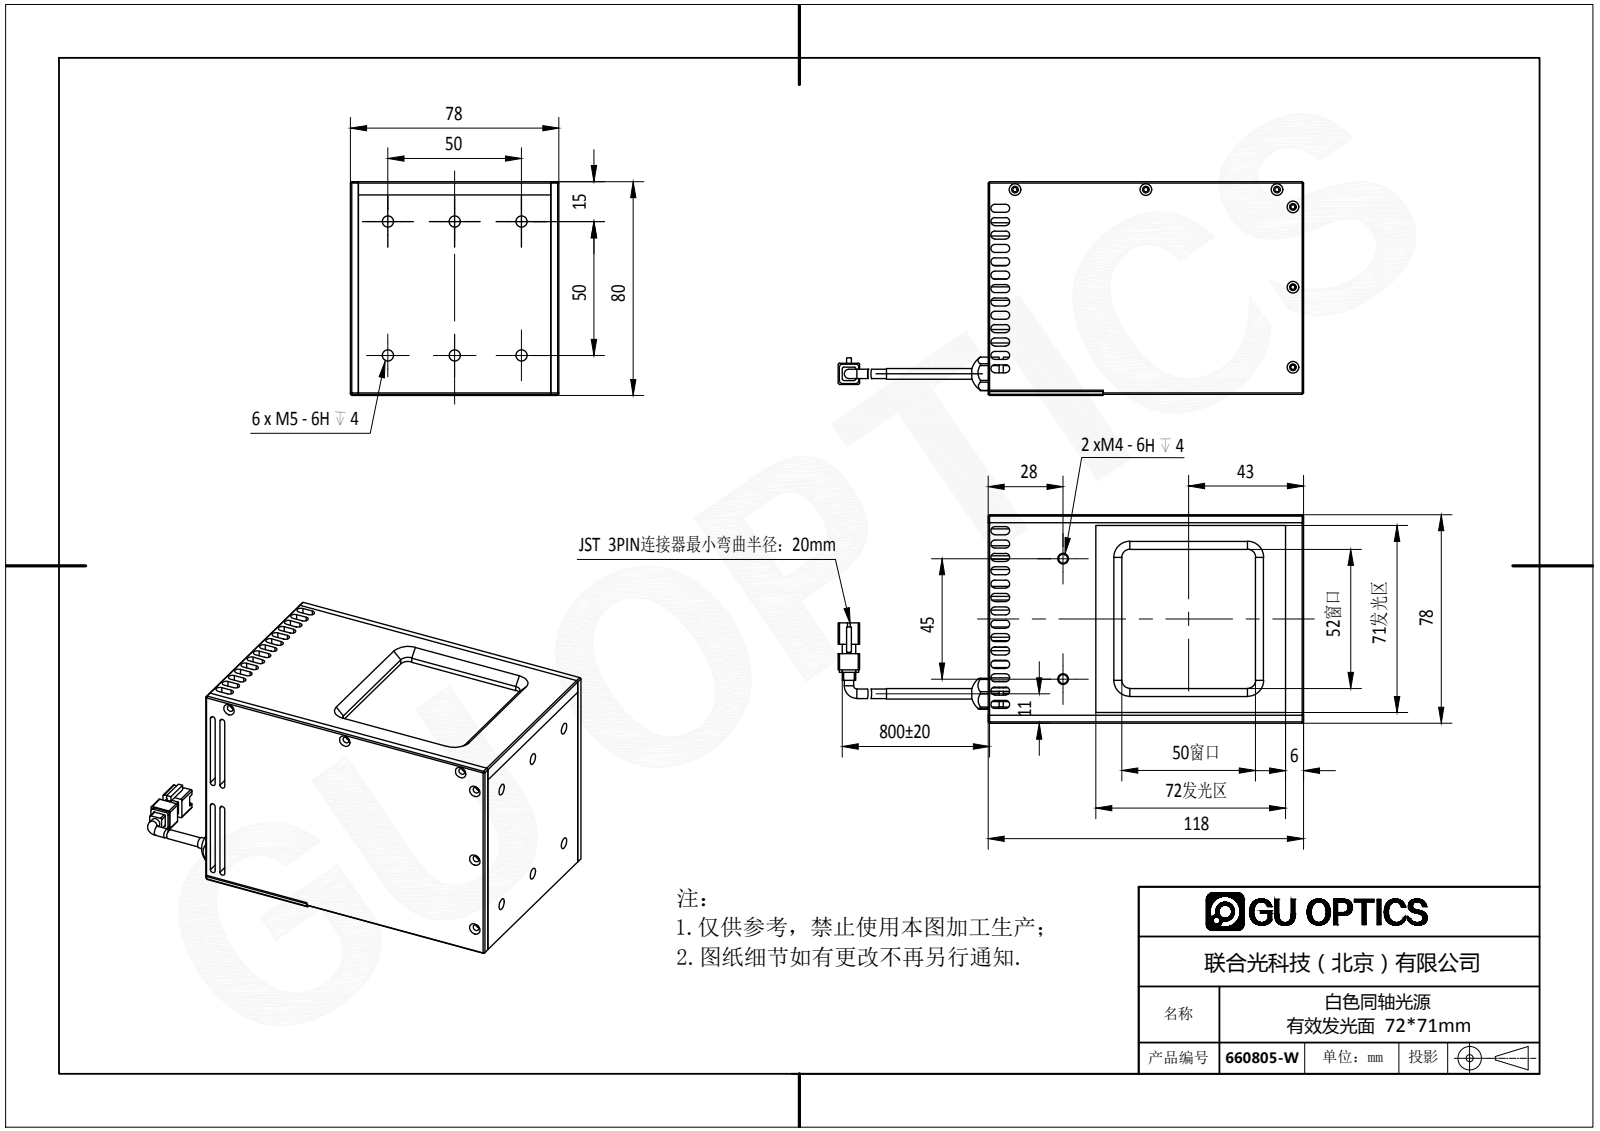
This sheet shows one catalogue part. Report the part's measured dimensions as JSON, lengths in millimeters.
{"step_written_by": "SolidWorks 2016 (AUTOMOTIVE_DESIGN)", "units": "millimeters", "bodies": {"solids": 23, "faces": 1600, "planar": 1165, "cylindrical": 278, "other": 157}, "overall_size": [151.44, 80.2, 78], "volume_mm3": 196586, "surface_area_mm2": 164600, "round_holes": [[2.4, 16], [1.6, 15], [2, 9], [4.2, 6], [7, 4], [3.8, 1], [6.8, 1], [9, 1]], "round_bosses_or_shafts": [[3.5, 2], [9.76, 1], [8, 1], [4, 1]], "partial_cylinders_radius": [[1.5, 54], [1, 12], [0.5, 8], [2, 4], [3, 4], [0.8, 1], [6.25, 1]], "face_to_face_distances": [1, 4, 74, 6, 75, 78, 100, 3, 2, 70], "hole_center_spacings": [50, 17.5, 25, 55.9, 75.07, 70, 73, 1.1]}
